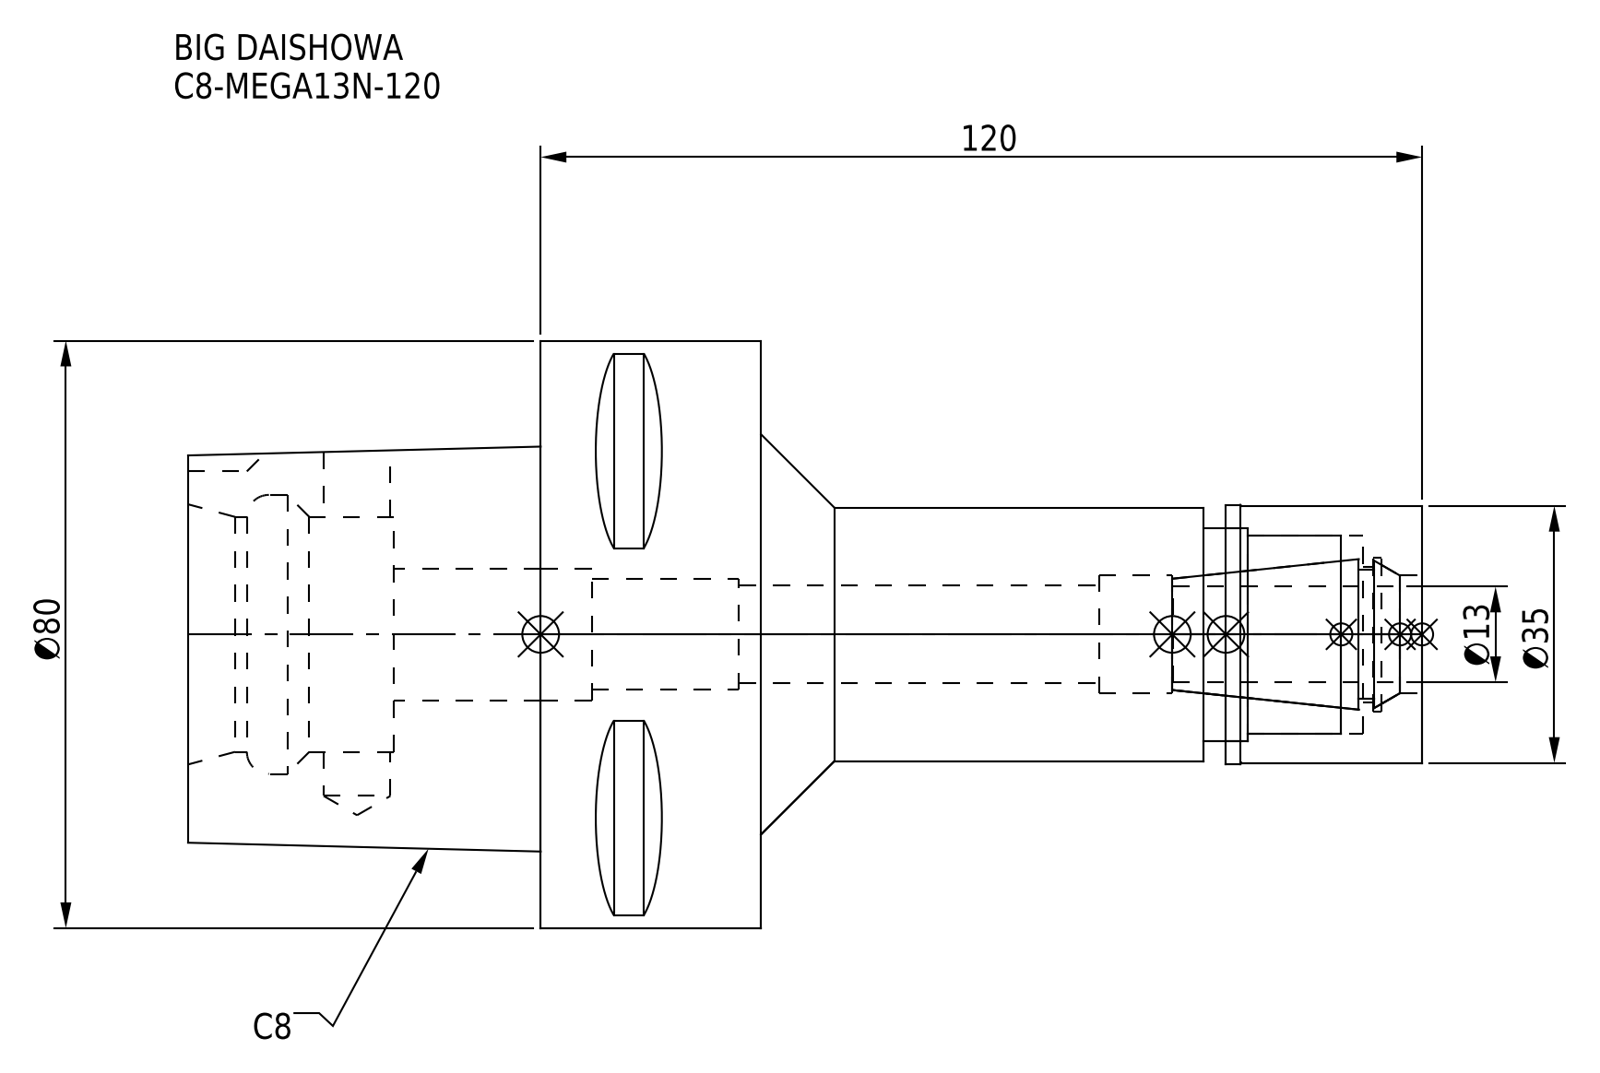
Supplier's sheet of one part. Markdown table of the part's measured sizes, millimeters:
| quantity | value |
| --- | --- |
| part name | C8-MEGA13N-120-130.stp; C8-MEGA13N-120-130-FreeParts; MGN13_1.stp; C8-MEGA13N-120 (+3 more) |
| STEP written by | SolidWorks 2019 (CONFIG_CONTROL_DESIGN) |
| units | millimeters |
| bodies | 2 solids, 98 faces (39 planar, 41 cylindrical, 18 other) |
| overall size | 168 × 80 × 80 |
| volume | 292 023 mm³ |
| surface area | 49 711 mm² |
| round holes (diameter × count) | 9.1 × 1, 13.3 × 1, 15 × 1, 16 × 1, 18 × 1, 18.5 × 1, 21 × 1, 27 × 1, 29 × 1, 32 × 1, 38 × 1 |
| round bosses / shafts (diameter × count) | 80 × 1, 35.3 × 1, 35 × 1, 34.5 × 1 |
| partial cylindrical surfaces (radius × count) | 6 × 1 |
| main face-to-face distances | 30, 78, 48, 90, 120, 168, 20, 140, 50, 28 |
